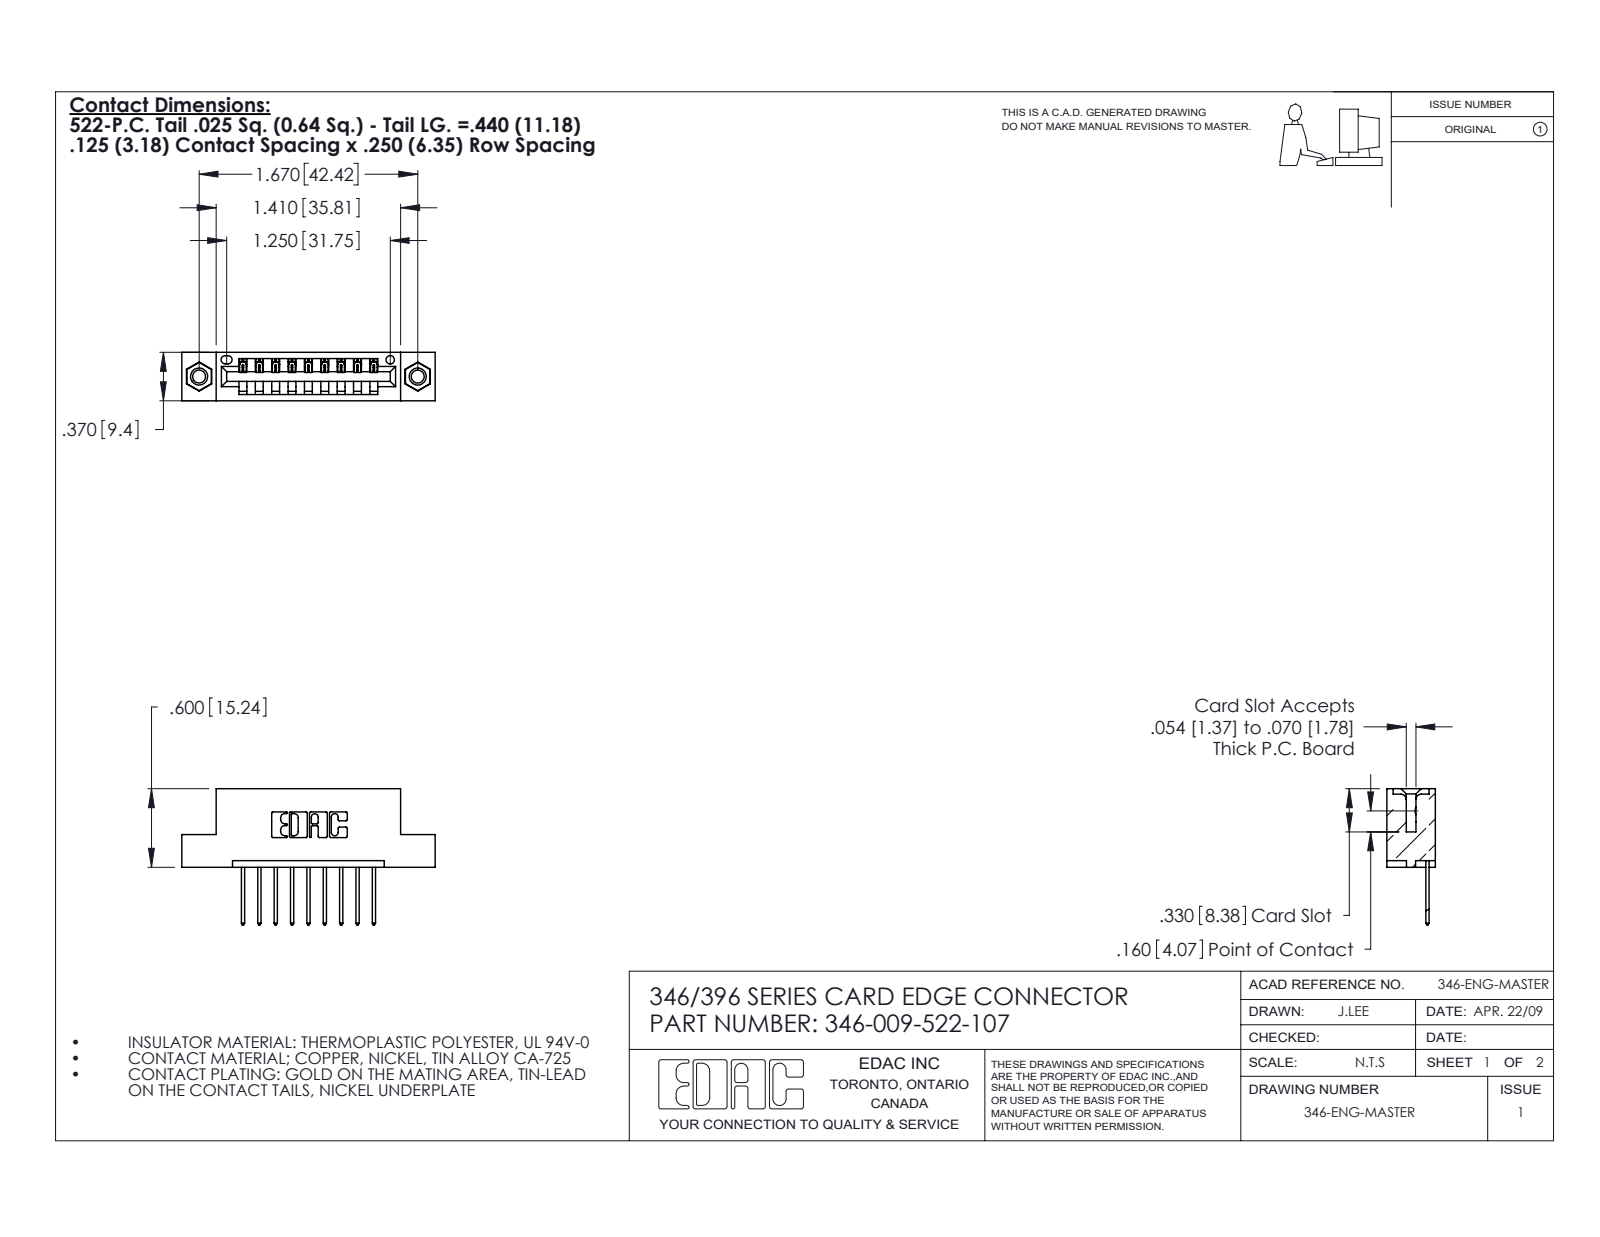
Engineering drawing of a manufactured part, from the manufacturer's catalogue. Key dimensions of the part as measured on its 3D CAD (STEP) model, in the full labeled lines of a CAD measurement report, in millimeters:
Part name (STEP PRODUCT): 346 Part_Flush Mounting Lugs - 0.156 Dia-TI; 346-009-522-107; 345-292-001_345-293-122; 345-250-001_345-250-005-103
STEP written by: SolidWorks 2020 (CONFIG_CONTROL_DESIGN)
Units: millimetres
Bodies: 12 solids, 704 faces (468 planar, 220 cylindrical, 16 other)
Overall size (bounding box): 49.1 × 26.4 × 9.4
Volume: 4 460 mm³ · Surface area: 5 292 mm²
Round holes (diameter × count): ⌀2.5 ×2, ⌀3.2 ×2, ⌀4 ×2, ⌀1.6 ×1
Round bosses / shafts (diameter × count): ⌀3.9 ×2
Partial cylindrical surfaces — rounded edges, fillets, slot ends (radius × count): R0.3 ×22, R0.2 ×18, R0.3 ×18, R0.2 ×6, R0.8 ×6, R0.7 ×3, R0.8 ×2, R1 ×2
Main face-to-face distances: 6.4, 1.2, 8.2, 9.4, 1.8, 7.6, 0.6, 3.8, 5.6, 2.5
Hole centre spacings: 6.2, 37.2, 42.4
